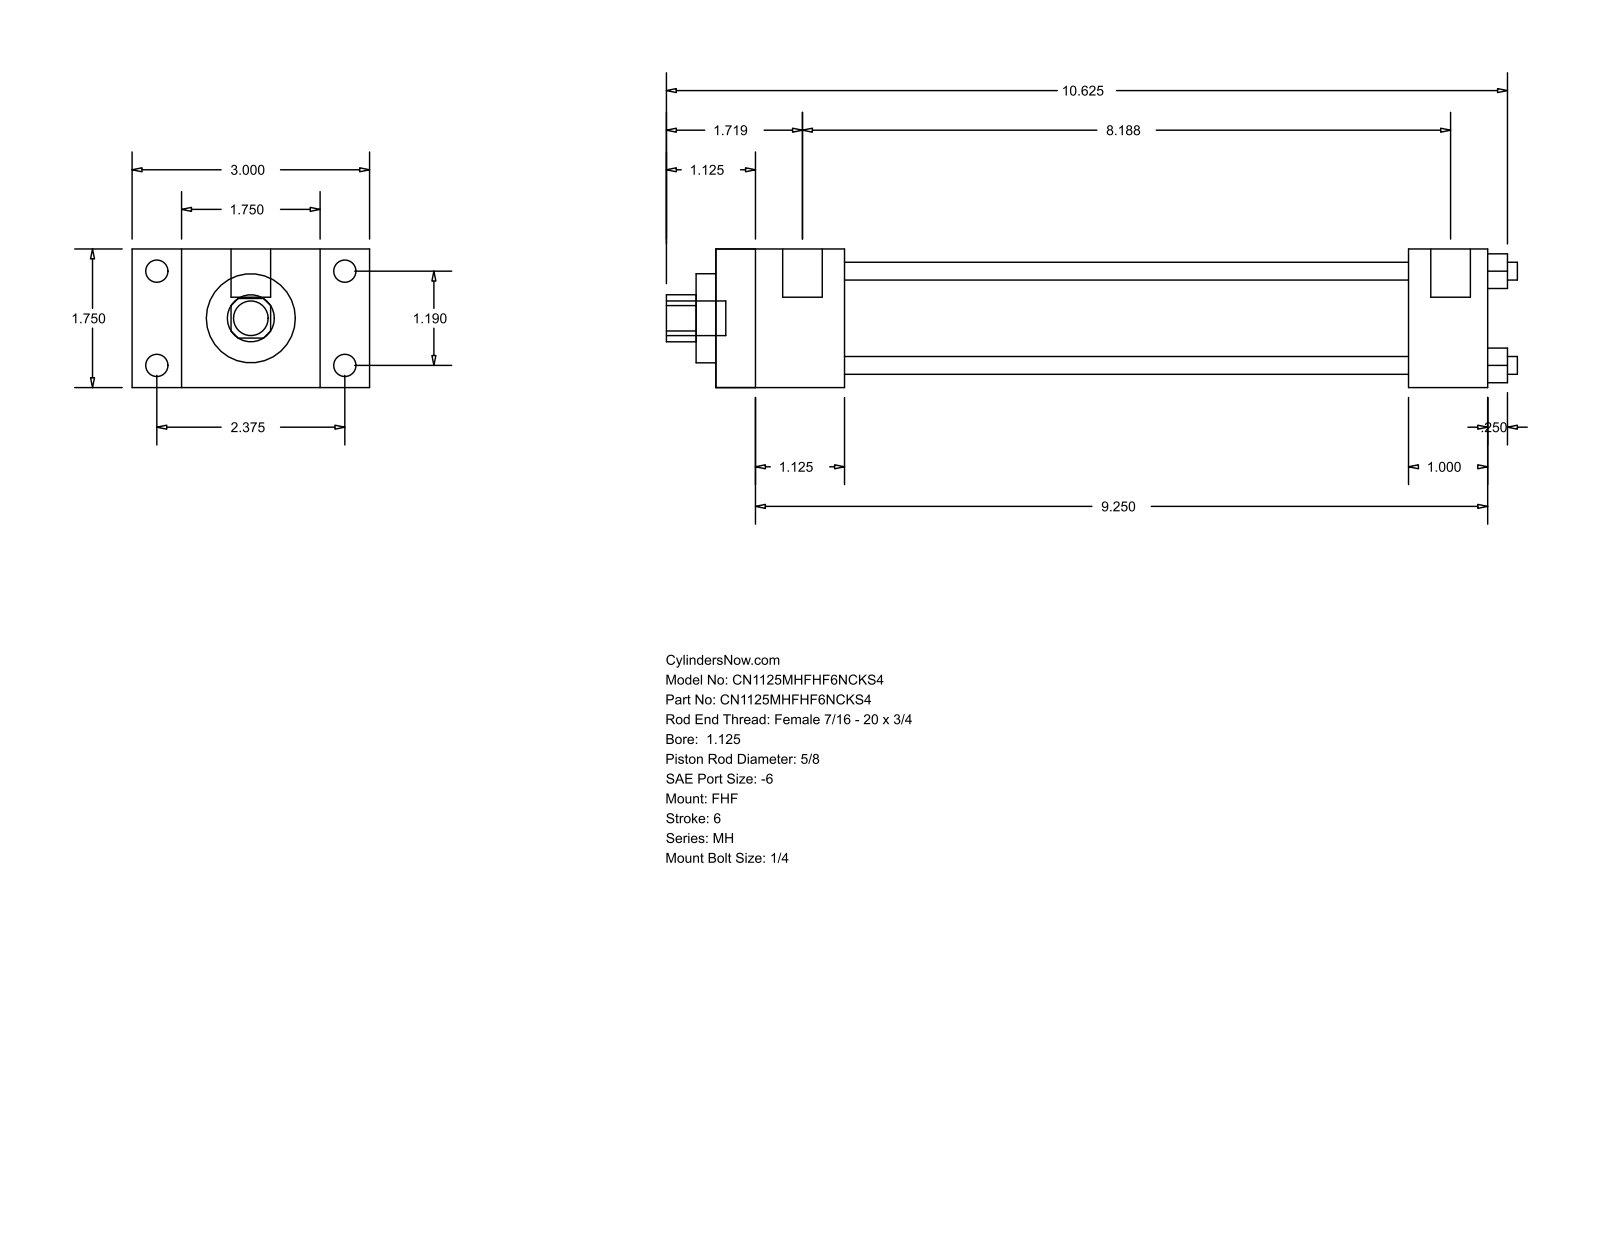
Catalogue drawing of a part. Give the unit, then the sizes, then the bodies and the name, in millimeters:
Units: millimetres
Overall size (bounding box): 273.05 × 76.2 × 44.45
Round holes (diameter × count): ⌀5.71 ×4, ⌀15.88 ×1, ⌀28.57 ×1, ⌀34.92 ×1
Round bosses / shafts (diameter × count): ⌀7.14 ×4, ⌀5.56 ×4, ⌀12.7 ×2, ⌀11.11 ×1
Partial cylindrical surfaces — rounded edges, fillets, slot ends (radius × count): R7.54 ×1
Main face-to-face distances: 44.46, 15.87, 60.33, 41.27, 76.2, 247.64, 206.37, 222.24, 180.97, 25.4
Hole centre spacings: 21.37, 30.22, 42.74
Bodies: 0 solids, 88 faces (60 planar, 28 cylindrical, 0 other)
Part name (STEP PRODUCT): MH_FHF__0112_0.625
STEP written by: GSSL Pune (CONFIG_CONTROL_DESIGN)
